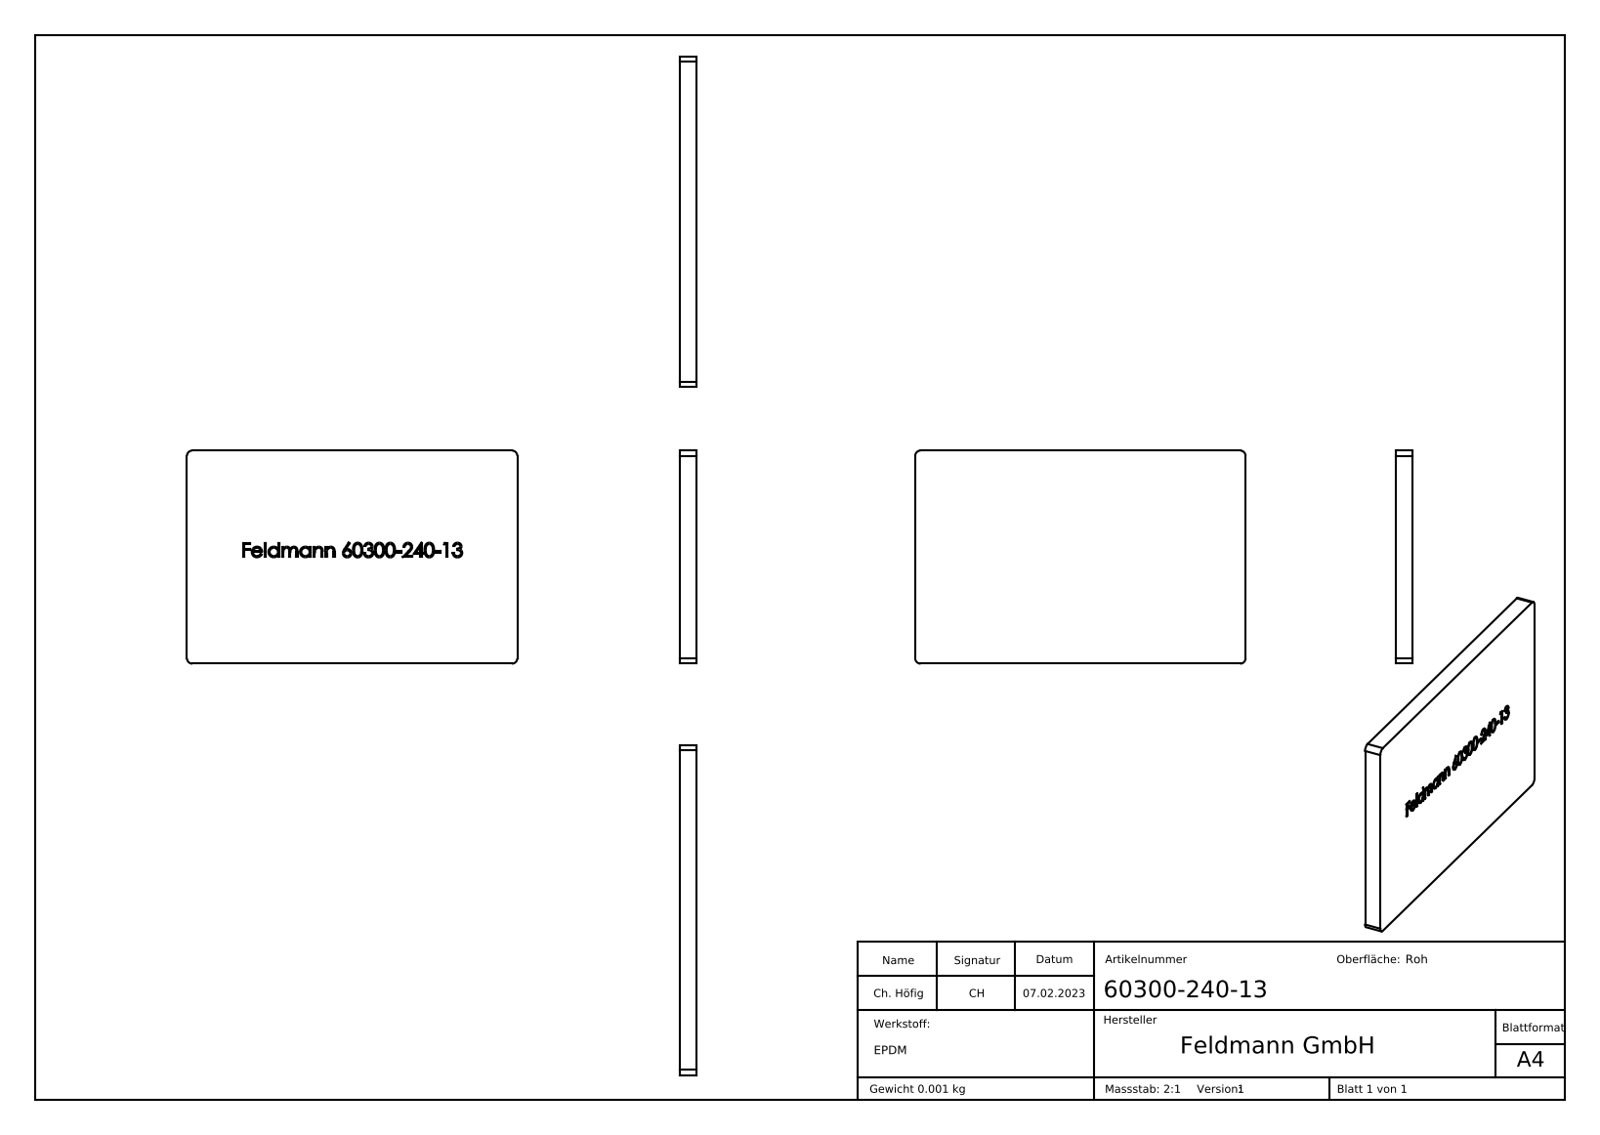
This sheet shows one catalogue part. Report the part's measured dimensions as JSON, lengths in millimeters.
{"part_name": "60300-240-13", "step_written_by": "SolidWorks 2018 (CONFIG_CONTROL_DESIGN)", "units": "millimeters", "bodies": {"solids": 1, "faces": 262, "planar": 131, "cylindrical": 4, "other": 127}, "overall_size": [31, 20, 1.62], "volume_mm3": 1003, "surface_area_mm2": 1414, "partial_cylinders_radius": [[0.5, 4]], "face_to_face_distances": [1.62, 20, 31, 1.52, 10, 0.39, 0.44, 17.05, 2.02, 0.58]}
